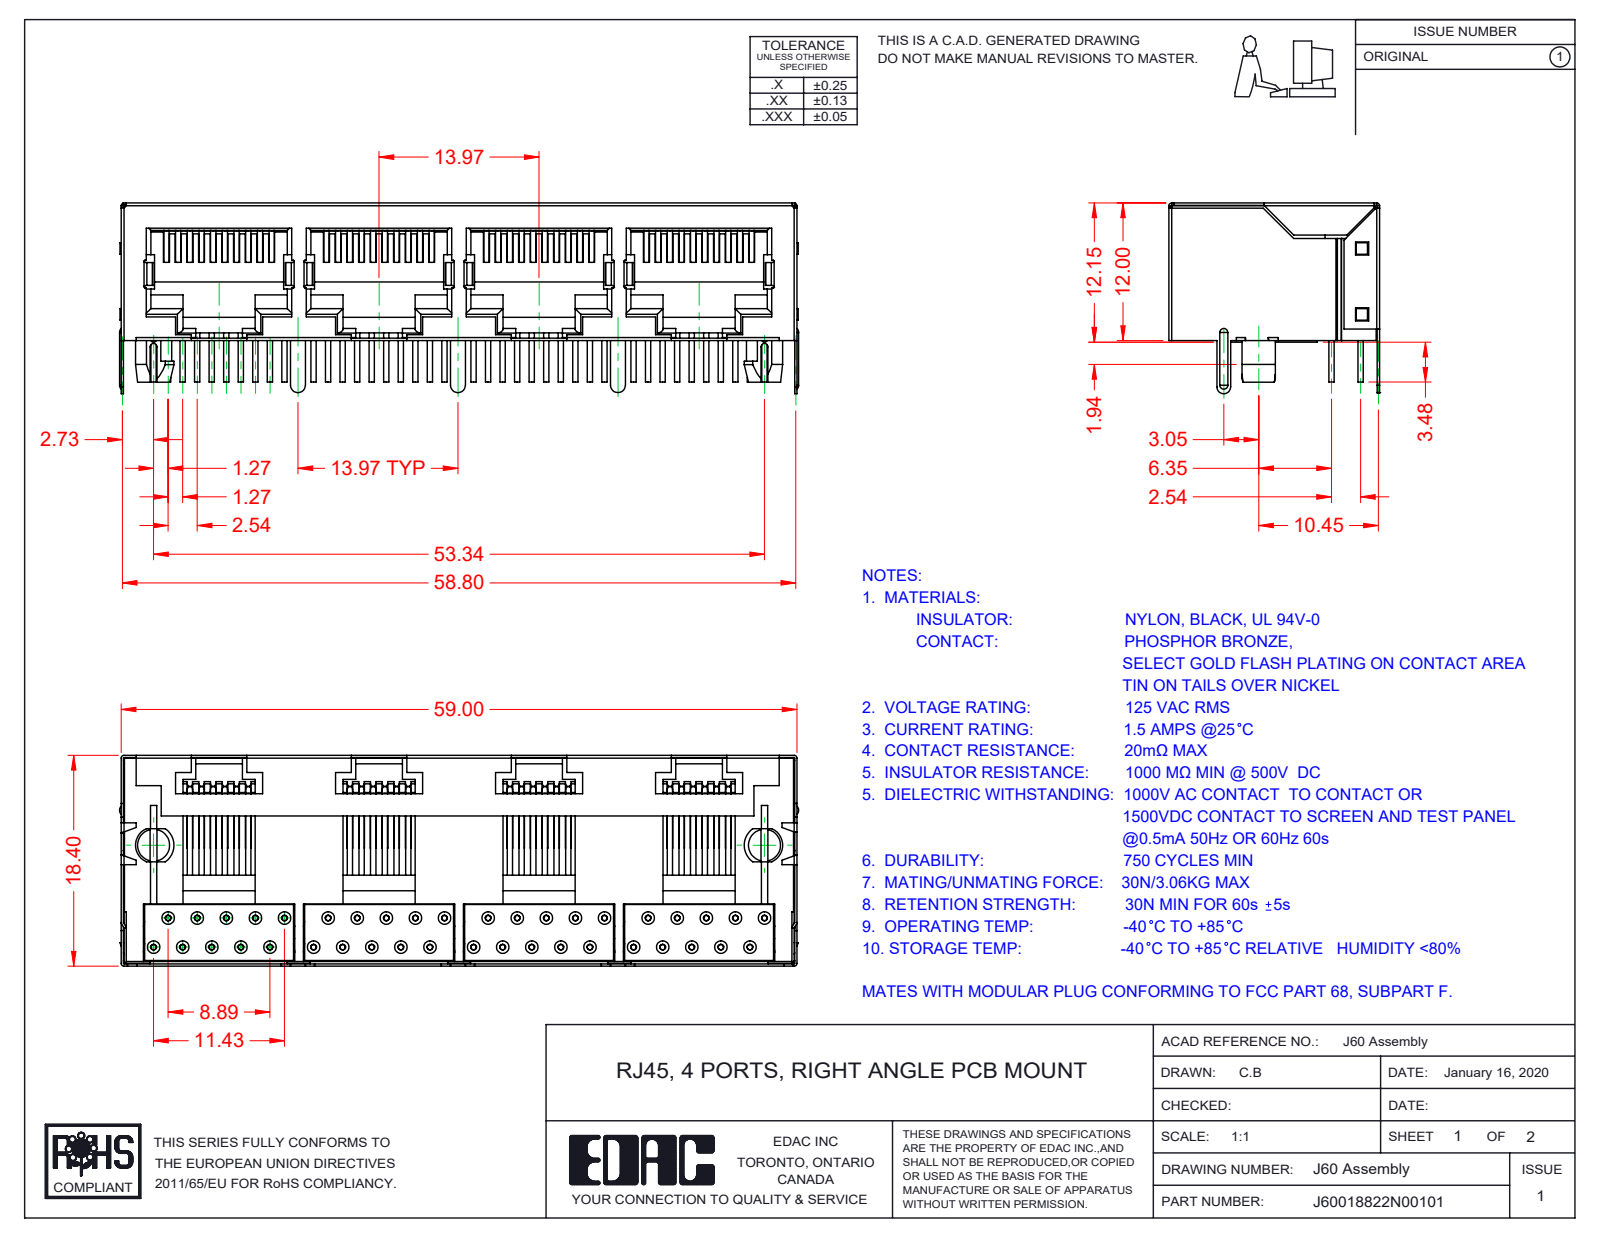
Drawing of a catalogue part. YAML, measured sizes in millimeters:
part_name: "60 Contacts_10P10C; 60 Shield; RJ60041122N00101; 60 Insulator"
step_written_by: "SolidWorks 2016 (CONFIG_CONTROL_DESIGN)"
units: millimeters
bodies: {solids: 42, faces: 2674, planar: 1505, cylindrical: 763, other: 406}
overall_size: [59.3, 18.4, 16.65]
volume: 7062
surface_area: 18987
round_holes:
  - {diameter: 0.5, count: 40}
  - {diameter: 1.1, count: 40}
round_bosses_or_shafts:
  - {diameter: 0.46, count: 120}
partial_cylinders:
  - {radius: 0.3, count: 26}
  - {radius: 0.25, count: 21}
  - {radius: 0.5, count: 18}
  - {radius: 0.1, count: 16}
  - {radius: 0.21, count: 10}
  - {radius: 0.8, count: 7}
  - {radius: 0.65, count: 3}
  - {radius: 0.28, count: 2}
face_to_face_distances: [0.5, 11.75, 11.55, 13.97, 2.19, 5.38, 5.18, 4.88, 18.2, 11.5]
hole_center_spacings: [2.84, 2.54, 4.58, 13.97, 5.08, 12.95, 15.45, 11.43]
